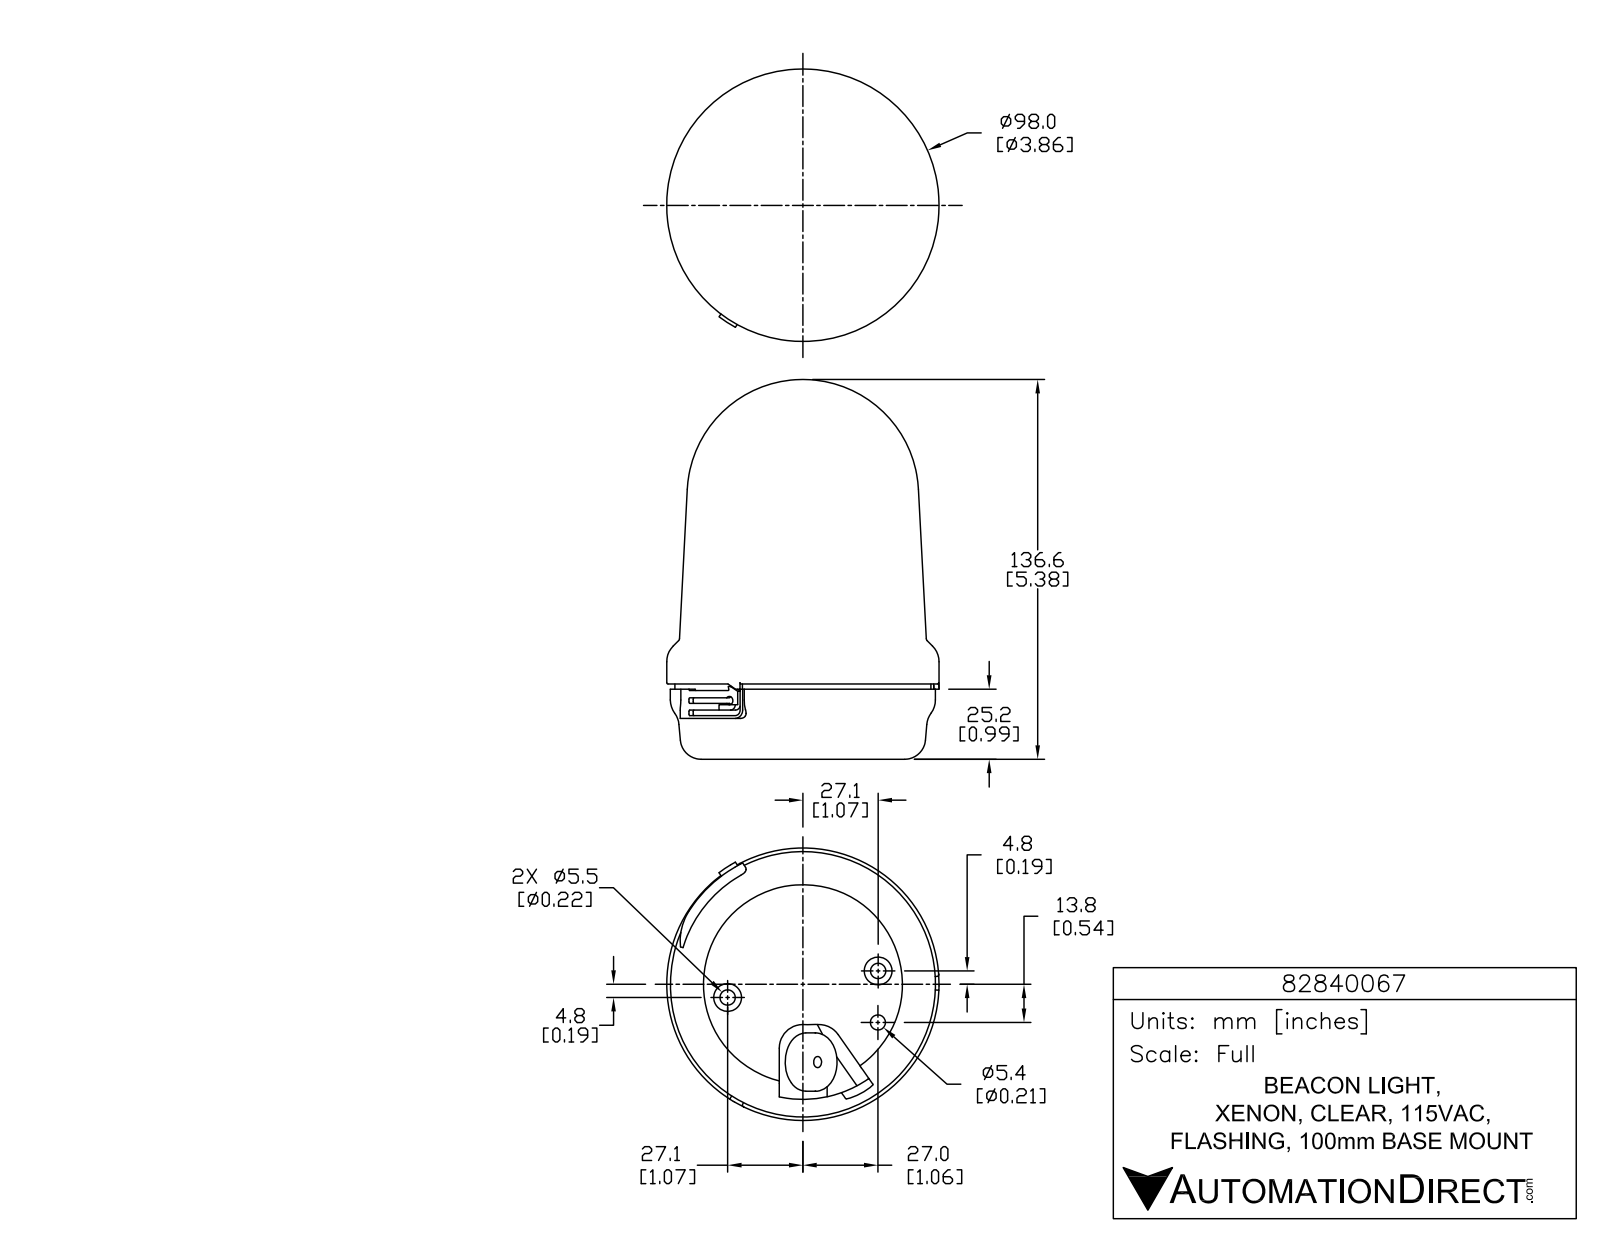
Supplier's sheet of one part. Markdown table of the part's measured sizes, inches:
| quantity | value |
| --- | --- |
| part name | 82840067 |
| STEP written by | SolidWorks 2015 (AUTOMOTIVE_DESIGN) |
| units | inches |
| bodies | 1 solid, 872 faces (566 planar, 204 cylindrical, 102 other) |
| overall size | 5.378 × 3.858 × 3.858 |
| volume | 44.69 in³ |
| surface area | 73.66 in² |
| round holes (diameter × count) | 0.059 × 3, 0.217 × 2, 0.157 × 1, 0.213 × 1, 2.819 × 1 |
| round bosses / shafts (diameter × count) | 0.339 × 3, 0.084 × 3, 0.394 × 2, 3.858 × 1, 3.756 × 1, 3.626 × 1, 0.827 × 1 |
| partial cylindrical surfaces (radius × count) | 0.005 × 9, 0.005 × 6, 0.012 × 6, 0.012 × 6, 0.012 × 6, 0.196 × 6, 0.02 × 5, 0.039 × 4 |
| main face-to-face distances | 1.045, 0.972, 0.073, 0.02, 0.992, 1.065, 0.236, 0.579, 0.559, 0.413 |
| hole center spacings | 1.083, 0.73, 1.193, 2.158, 2.165 |
